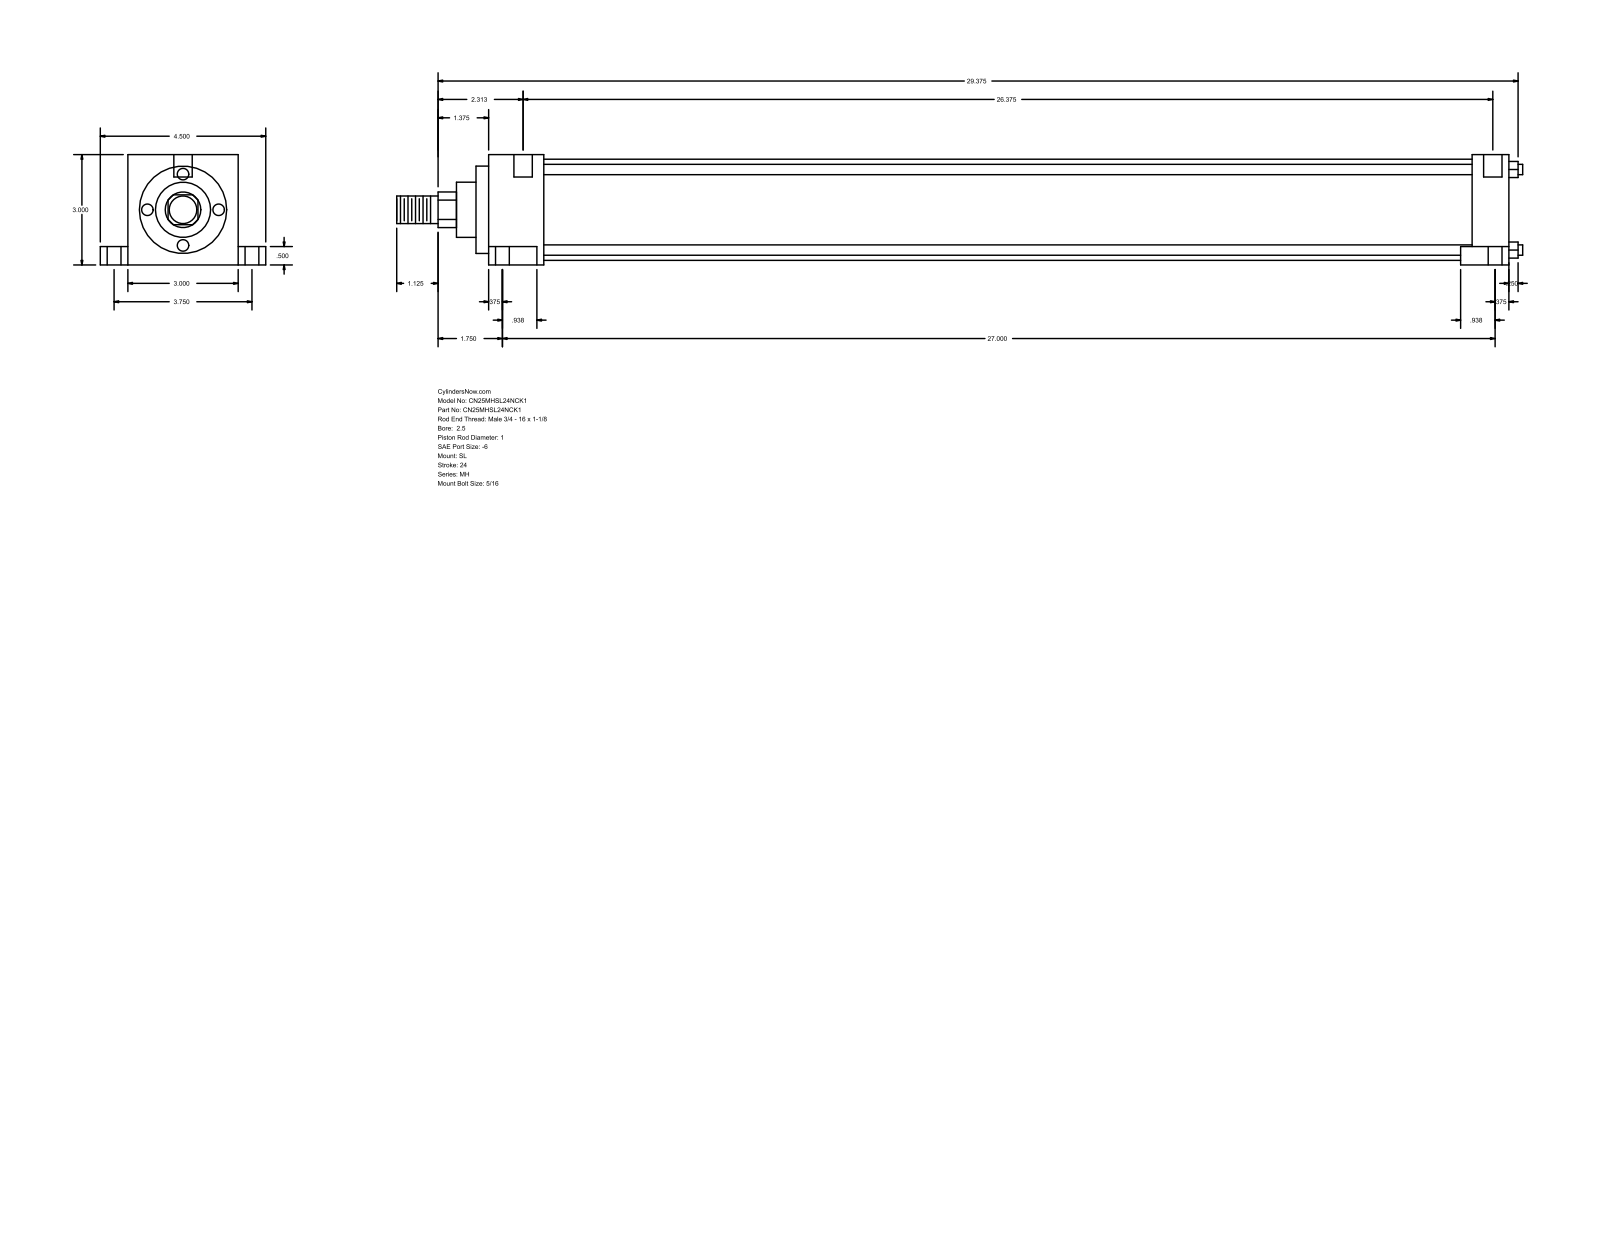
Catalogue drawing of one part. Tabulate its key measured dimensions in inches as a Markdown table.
| quantity | value |
| --- | --- |
| part name | MH_SL__0250_1 |
| STEP written by | GSSL Pune (CONFIG_CONTROL_DESIGN) |
| units | inches |
| bodies | 0 solids, 86 faces (61 planar, 25 cylindrical, 0 other) |
| overall size | 30.625 × 4.5 × 3 |
| round holes (diameter × count) | 0.219 × 2, 0.375 × 2, 0.625 × 2, 0.5 × 1 |
| round bosses / shafts (diameter × count) | 0.281 × 4, 2.75 × 1, 2.375 × 1, 1.5 × 1, 1 × 1, 0.75 × 1 |
| partial cylindrical surfaces (radius × count) | 0.484 × 1 |
| main face-to-face distances | 3, 1, 27.094, 28.094, 0.5, 2.5, 0.75, 3.75, 0.531, 27.625 |
| hole center spacings | 1.876, 0.125, 3.75 |
